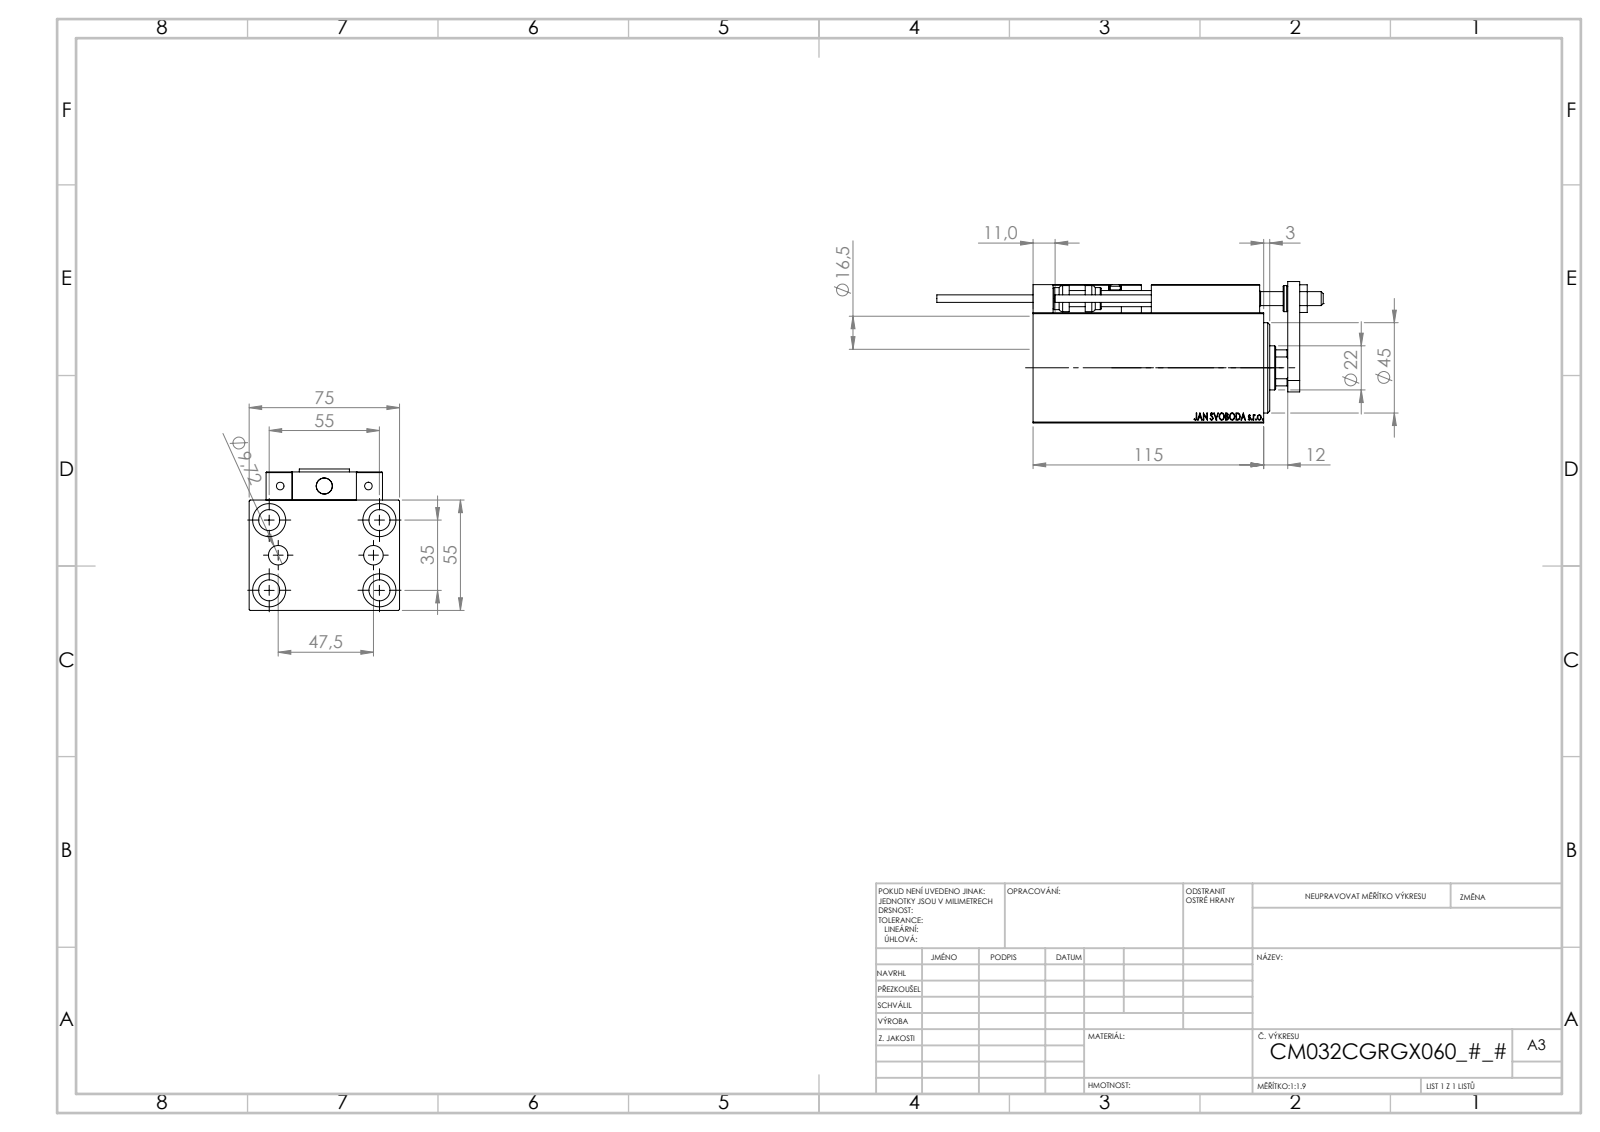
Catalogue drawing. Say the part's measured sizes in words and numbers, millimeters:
The part is named "NUT_D12; V450CM_C_Body; SWITCH DIM B,W; ZARAZKA (+7 more)". Its 3-D file was written by "SolidWorks 2019 (CONFIG_CONTROL_DESIGN)". It is 23 solids with 1278 faces: 560 planar, 184 cylindrical and 534 other. Overall it measures 192.7 by 75 by 70.5 millimeters. Its volume is 449 169 cubic millimeters and its surface area 105 723 square millimeters. Round holes: 6 of diameter 4, 5 of diameter 8, 5 of diameter 10.5, 5 of diameter 16.5, 4 of diameter 3.2, 2 of diameter 5, 2 of diameter 9.72, 1 of diameter 7, 1 of diameter 22, 1 of diameter 25.5, 1 of diameter 32, 1 of diameter 34. Round bosses or shafts: 2 of diameter 5, 2 of diameter 3.8, 1 of diameter 13, 1 of diameter 11. Partial cylindrical surfaces (rounded edges, fillets, slot ends): 30 of radius 0.3, 2 of radius 3, 1 of radius 10.5. The main face-to-face distances are 55, 75, 14, 5, 69, 10, 12, 25, 3, 18. The hole center spacings are 17.9, 32.6, 54.16, 11.37, 20, 23.75, 29.59, 29.69.
